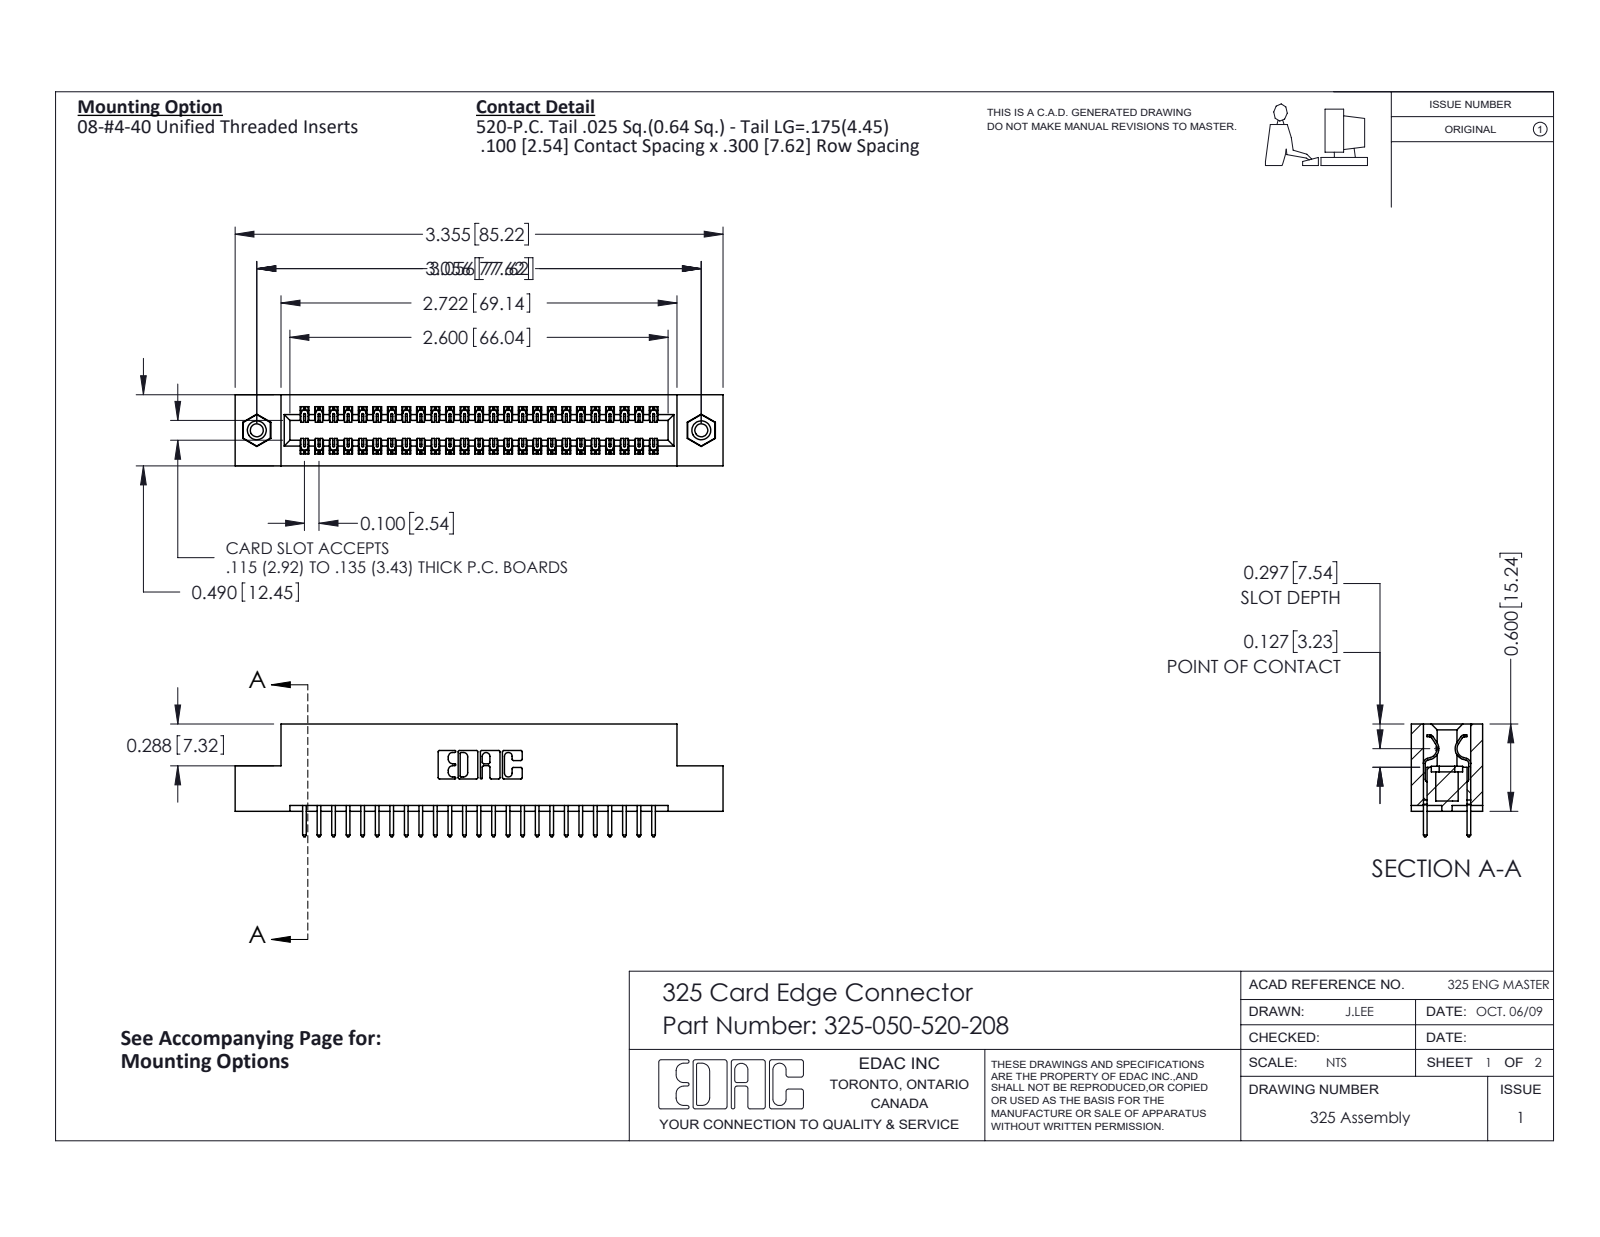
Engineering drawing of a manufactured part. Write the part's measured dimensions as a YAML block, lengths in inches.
part_name: "325-050-520-208; 325 Part_TI; 345-250-001_345-250-003-102; 325-292-001_325-293-120"
step_written_by: "SolidWorks 2016 (CONFIG_CONTROL_DESIGN)"
units: inches
bodies: {solids: 53, faces: 2774, planar: 1902, cylindrical: 856, other: 16}
overall_size: [3.355, 0.775, 0.49]
volume: 0.661
surface_area: 19.57
round_holes:
  - {diameter: 0.089, count: 2}
  - {diameter: 0.125, count: 2}
  - {diameter: 0.16, count: 2}
round_bosses_or_shafts:
  - {diameter: 0.155, count: 2}
partial_cylinders:
  - {radius: 0.006, count: 75}
  - {radius: 0.01, count: 50}
  - {radius: 0.01, count: 22}
  - {radius: 0.007, count: 6}
  - {radius: 0.031, count: 6}
  - {radius: 0.026, count: 3}
  - {radius: 0.014, count: 2}
  - {radius: 0.022, count: 2}
face_to_face_distances: [0.083, 0.407, 0.3, 0.49, 0.107, 0.383, 0.025, 0.325, 0.04, 0.275]
hole_center_spacings: [3.056]
